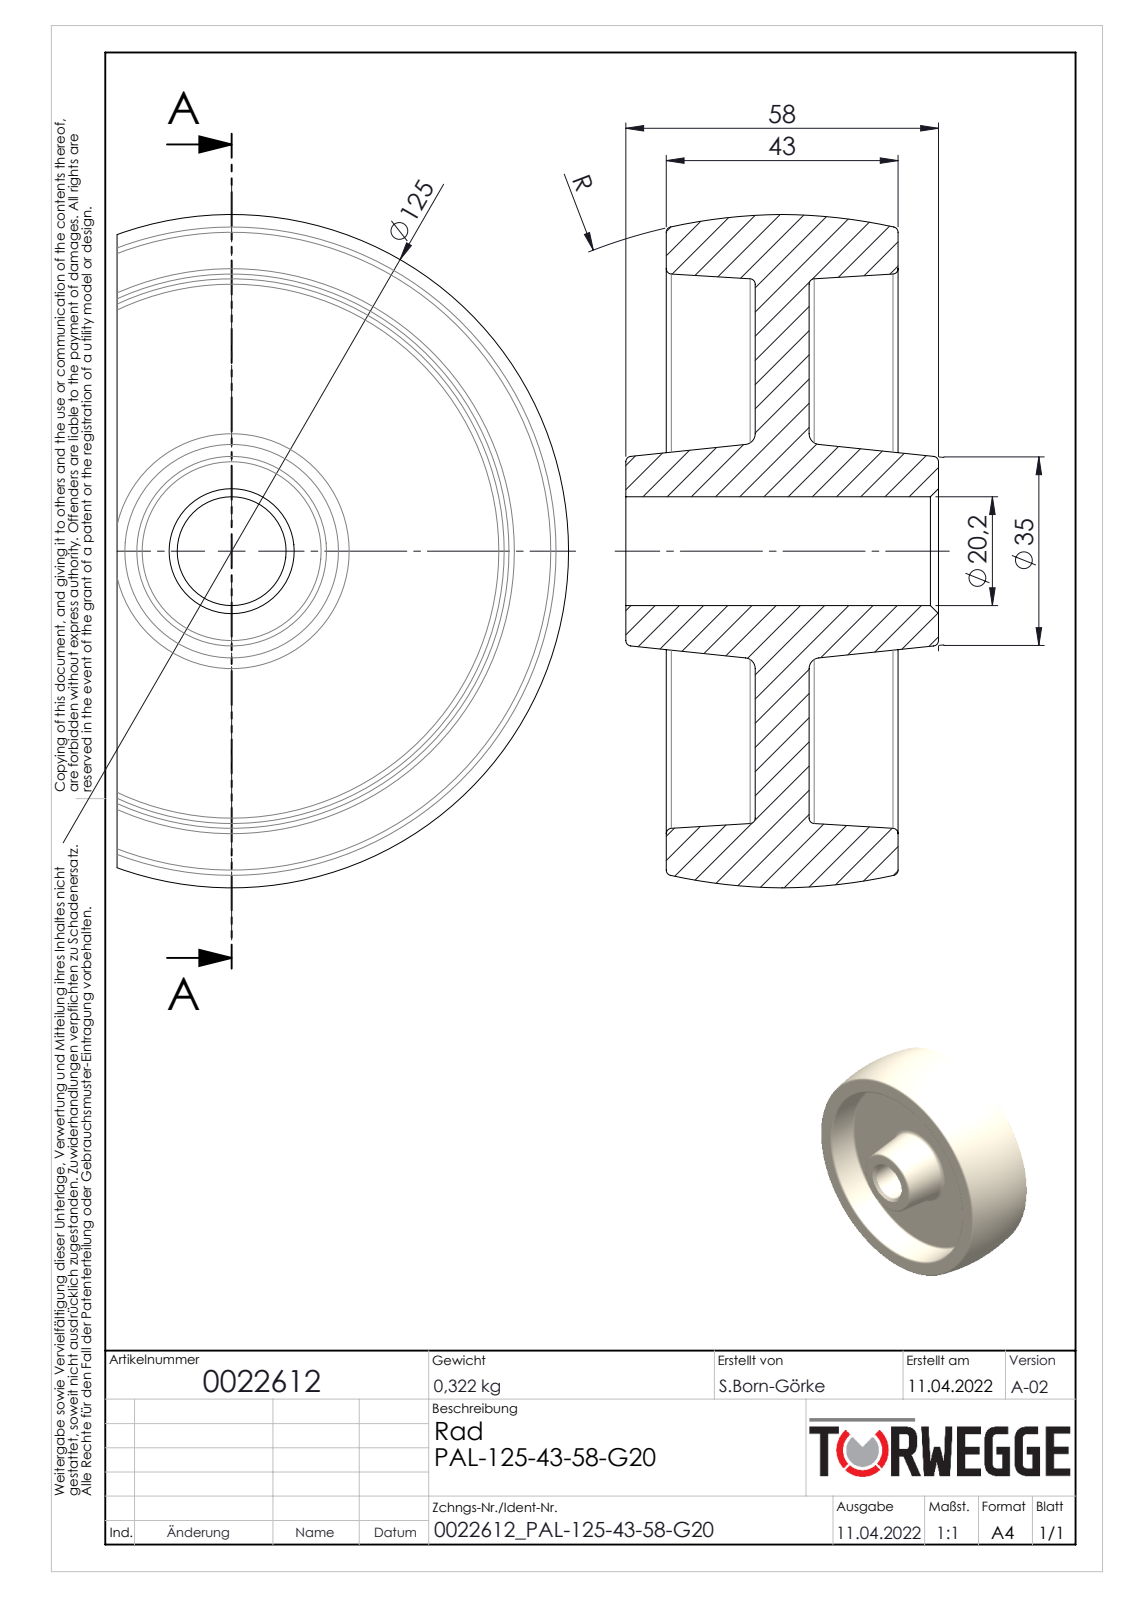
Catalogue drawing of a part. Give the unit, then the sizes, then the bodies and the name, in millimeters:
Units: millimetres
Overall size (bounding box): 125 × 125 × 58
Round holes (diameter × count): ⌀20.2 ×1
Main face-to-face distances: 10, 16.5, 26.5, 43, 7.5, 24, 34, 50.5, 58
Volume: 278 222 mm³ · Surface area: 56 547 mm²
Bodies: 1 solid, 42 faces (6 planar, 2 cylindrical, 34 other)
Part name (STEP PRODUCT): 0022612
STEP written by: SolidWorks 2020 (AUTOMOTIVE_DESIGN)
